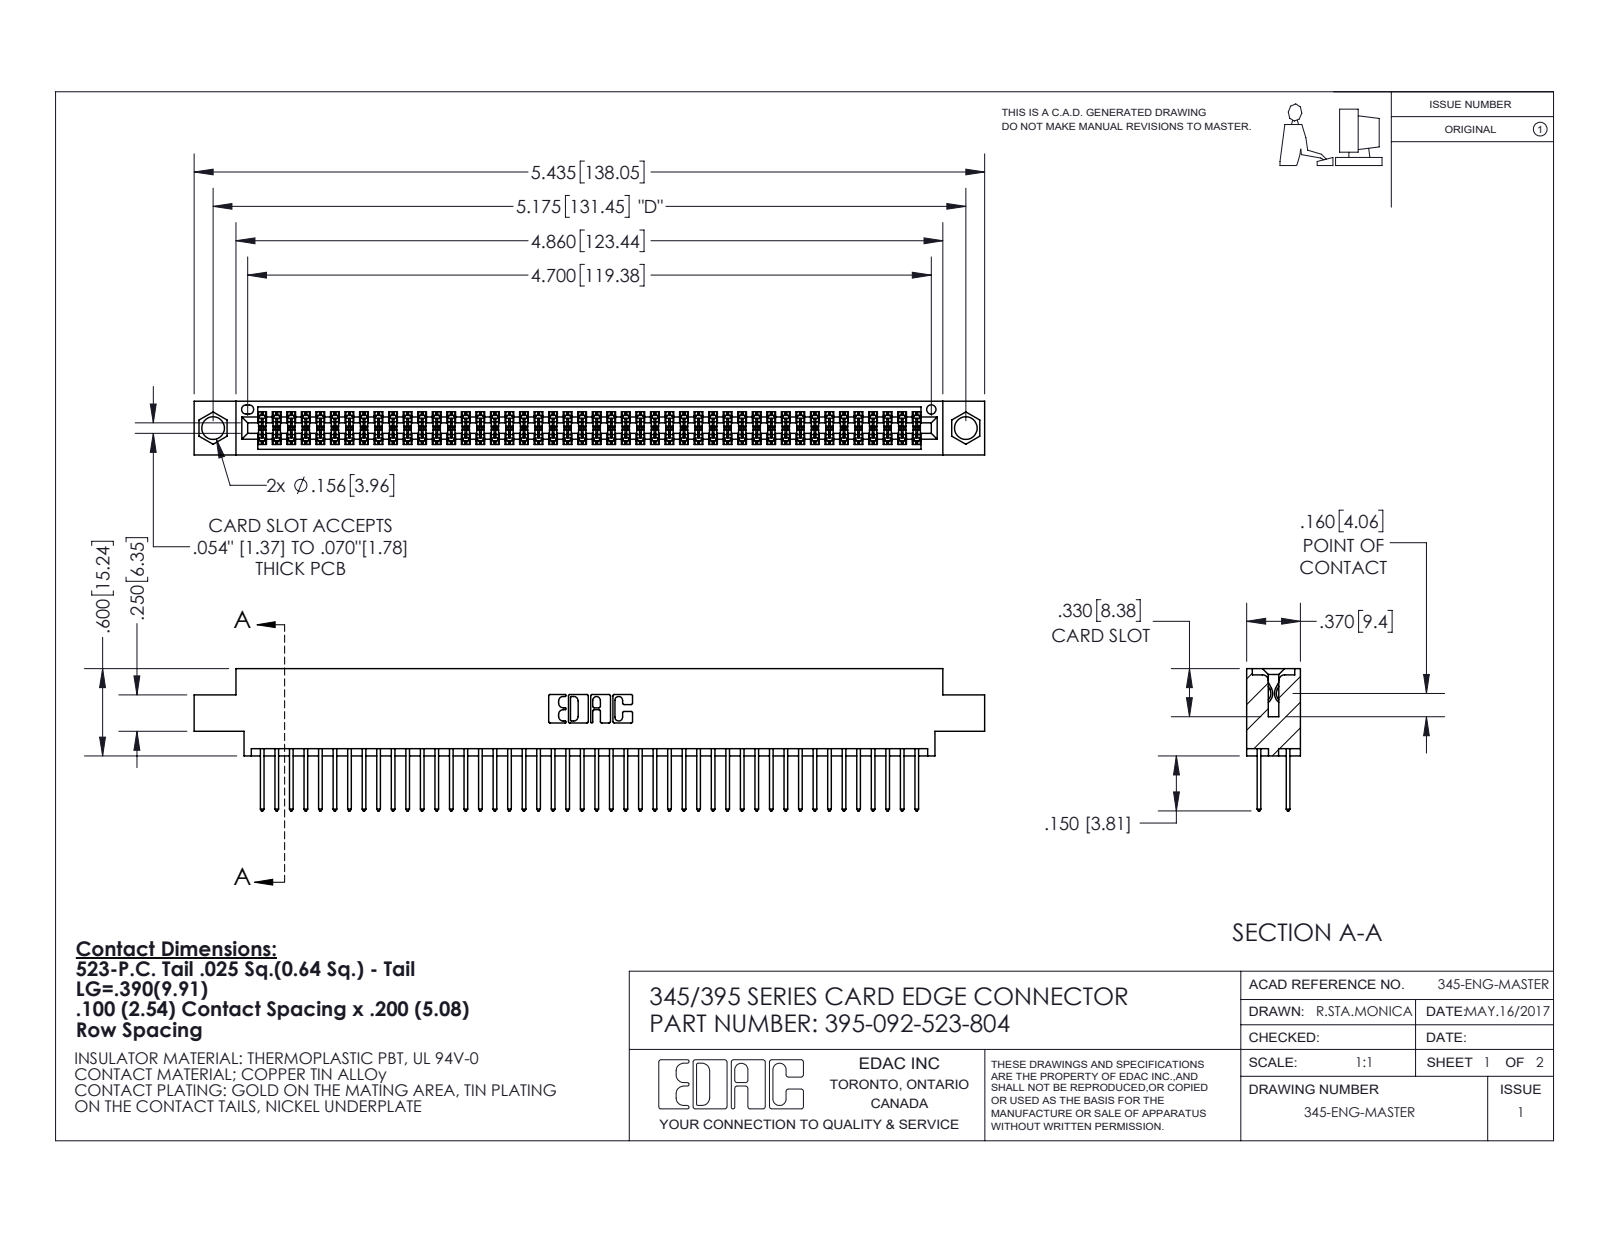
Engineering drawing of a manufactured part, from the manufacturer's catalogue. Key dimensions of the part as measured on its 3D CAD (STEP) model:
Part name (STEP PRODUCT): 345-292-001_345-293-123; 395-092-523-804; 345 Part_0.170 Offset - 0.156 Dia-TI
STEP written by: SolidWorks 2020 (CONFIG_CONTROL_DESIGN)
Units: inches
Bodies: 93 solids, 4744 faces (3134 planar, 1610 cylindrical, 0 other)
Overall size (bounding box): 5.435 × 0.977 × 0.37
Volume: 0.819 in³ · Surface area: 32.16 in²
Round holes (diameter × count): ⌀0.156 ×2, ⌀0.064 ×1
Partial cylindrical surfaces — rounded edges, fillets, slot ends (radius × count): R0.006 ×184, R0.01 ×92, R0.01 ×22, R0.007 ×6, R0.031 ×6, R0.026 ×3, R0.014 ×2, R0.019 ×2
Main face-to-face distances: 0.072, 0.298, 0.2, 0.098, 0.272, 0.025, 0.37, 0.225, 0.175, 0.149
Hole centre spacings: 0.27, 4.939, 5.175
